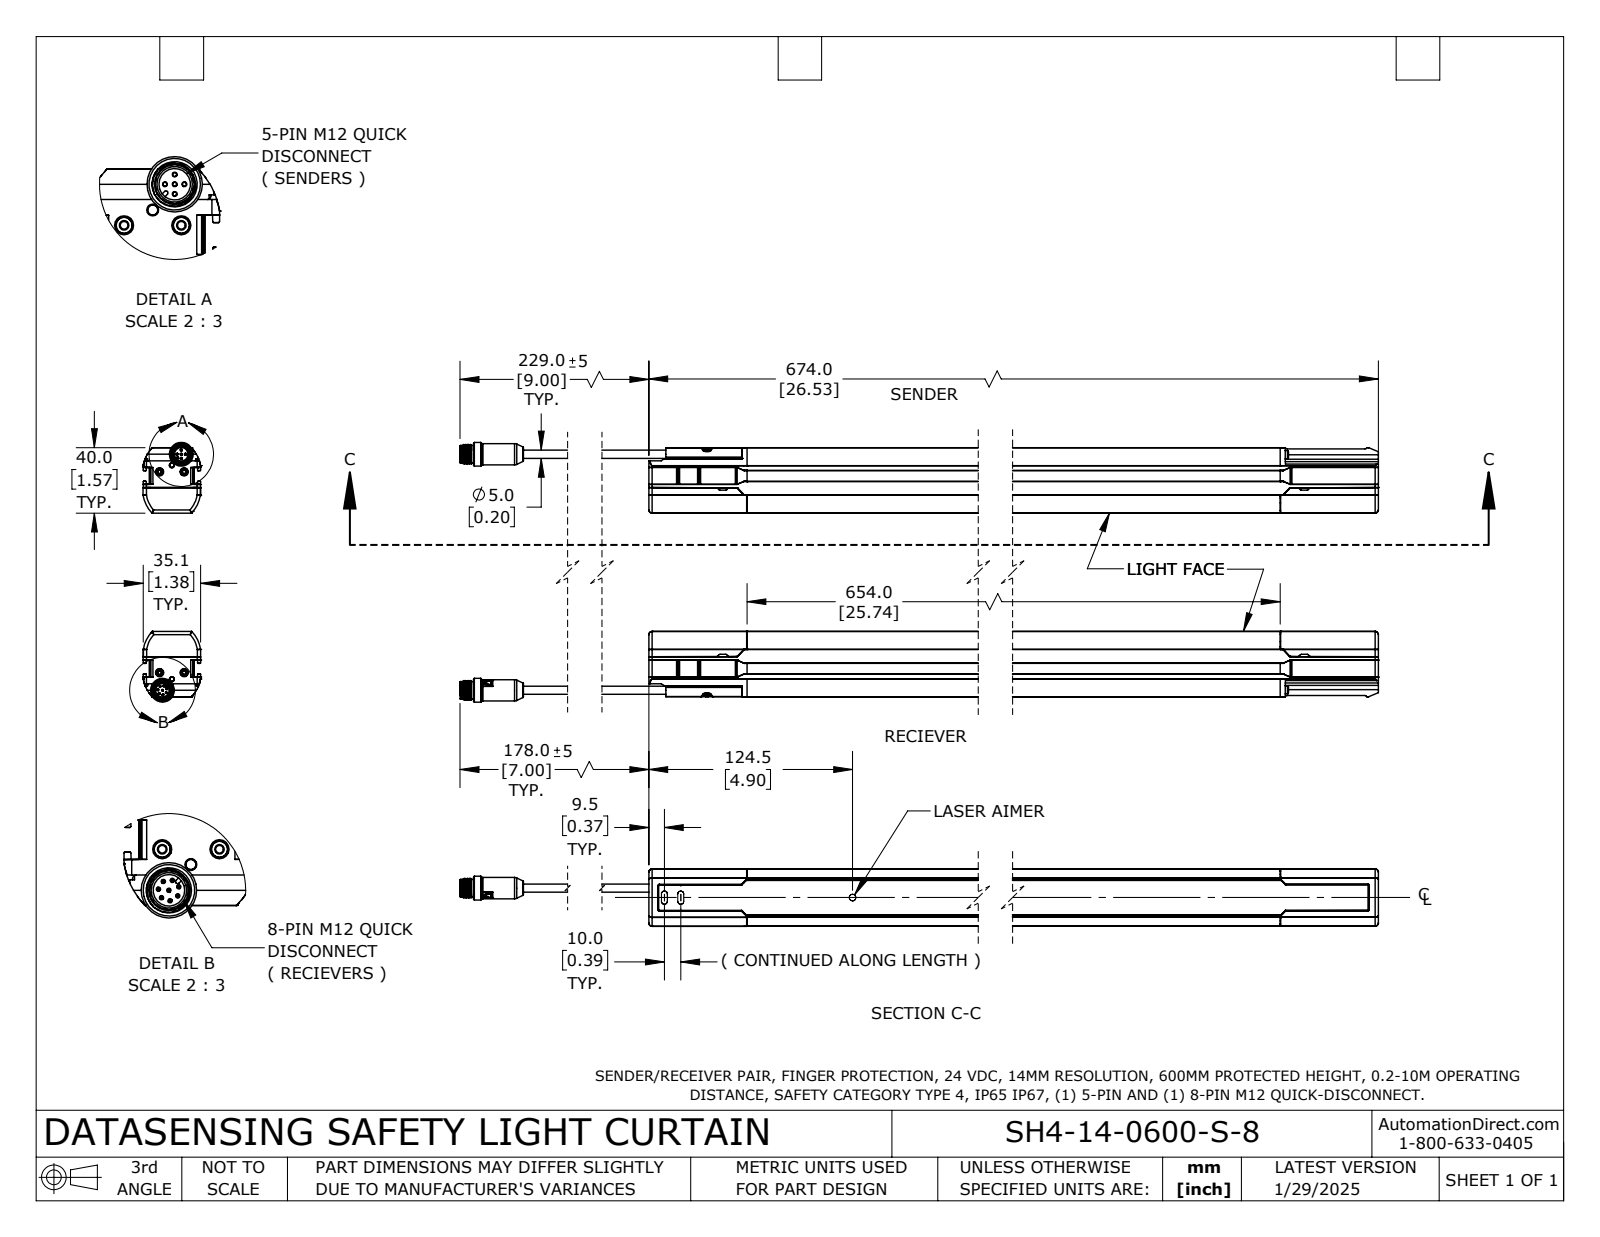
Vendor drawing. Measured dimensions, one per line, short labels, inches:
name: 957920059
written by: SolidWorks 2024 (AUTOMOTIVE_DESIGN)
unit: in
bodies: 4 solids, 2608 faces (1186 planar, 784 cylindrical, 638 other)
size: 32.967 × 6.249 × 1.384
volume: 86.57 in³; area: 429.8 in²
holes: 6× ⌀0.079, 6× ⌀0.118, 6× ⌀0.197, 2× ⌀0.101, 2× ⌀0.101, 2× ⌀0.101, 2× ⌀0.101, 2× ⌀0.325, 2× ⌀0.382, 2× ⌀0.407, 2× ⌀0.425, 1× ⌀0.11
bosses: 10× ⌀0.197, 8× ⌀0.087, 8× ⌀0.031, 6× ⌀0.172, 5× ⌀0.039, 4× ⌀0.217, 2× ⌀0.571, 2× ⌀0.512
rounds: 172× R0.01, 72× R0.016, 50× R0.02, 36× R0.008, 26× R0.031, 16× R0.047, 12× R0.031, 12× R0.079
face distances: 1.496, 4.496, 3, 0.028, 1.378, 5.992, 0.156, 1.222, 1.067, 0.079
hole spacings: 4.831, 0.591, 0.866, 4.867, 5.482, 0.585, 0.59, 0.591
